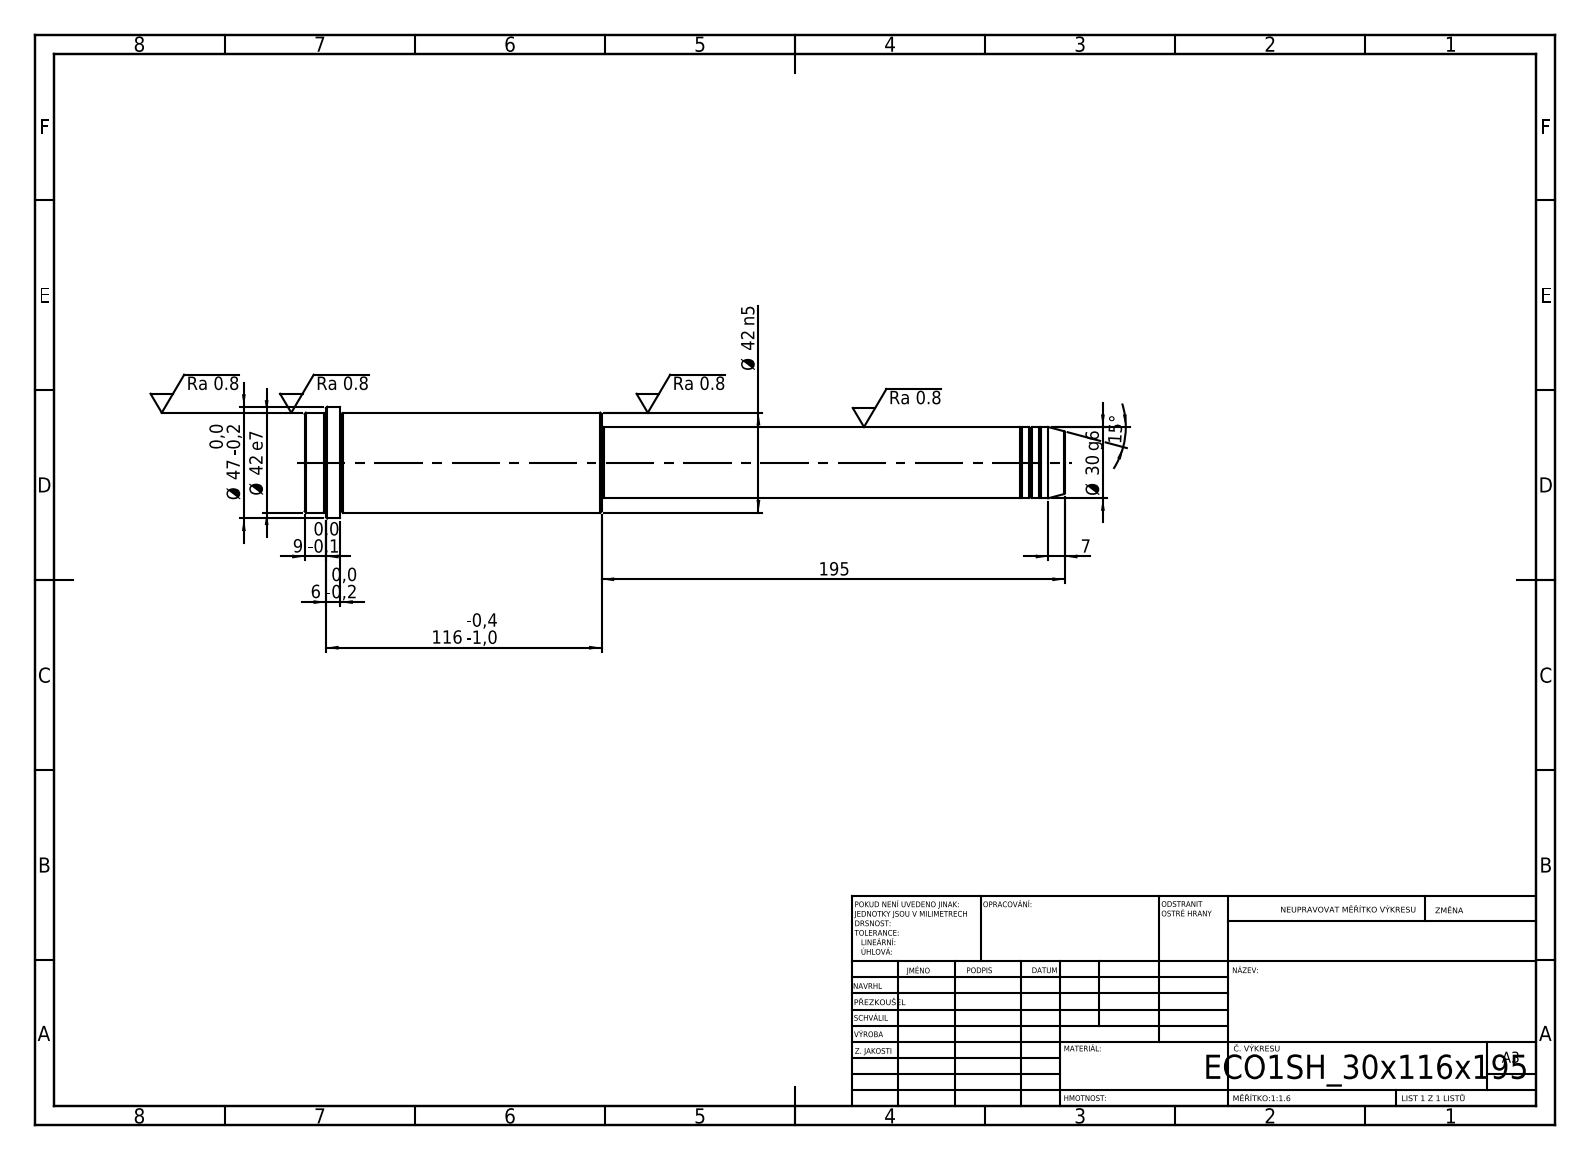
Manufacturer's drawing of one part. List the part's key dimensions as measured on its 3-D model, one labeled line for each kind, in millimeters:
STEP written by: SolidWorks 2019 (CONFIG_CONTROL_DESIGN)
Units: millimetres
Bodies: 1 solid, 52 faces (6 planar, 16 cylindrical, 30 other)
Overall size (bounding box): 320 × 47 × 47
Volume: 312 210 mm³ · Surface area: 38 506 mm²
Round bosses / shafts (diameter × count): ⌀47 ×1, ⌀42 ×1, ⌀30 ×1, ⌀29 ×1
Main face-to-face distances: 125, 195, 320, 305, 110, 15, 311, 116, 6, 9
